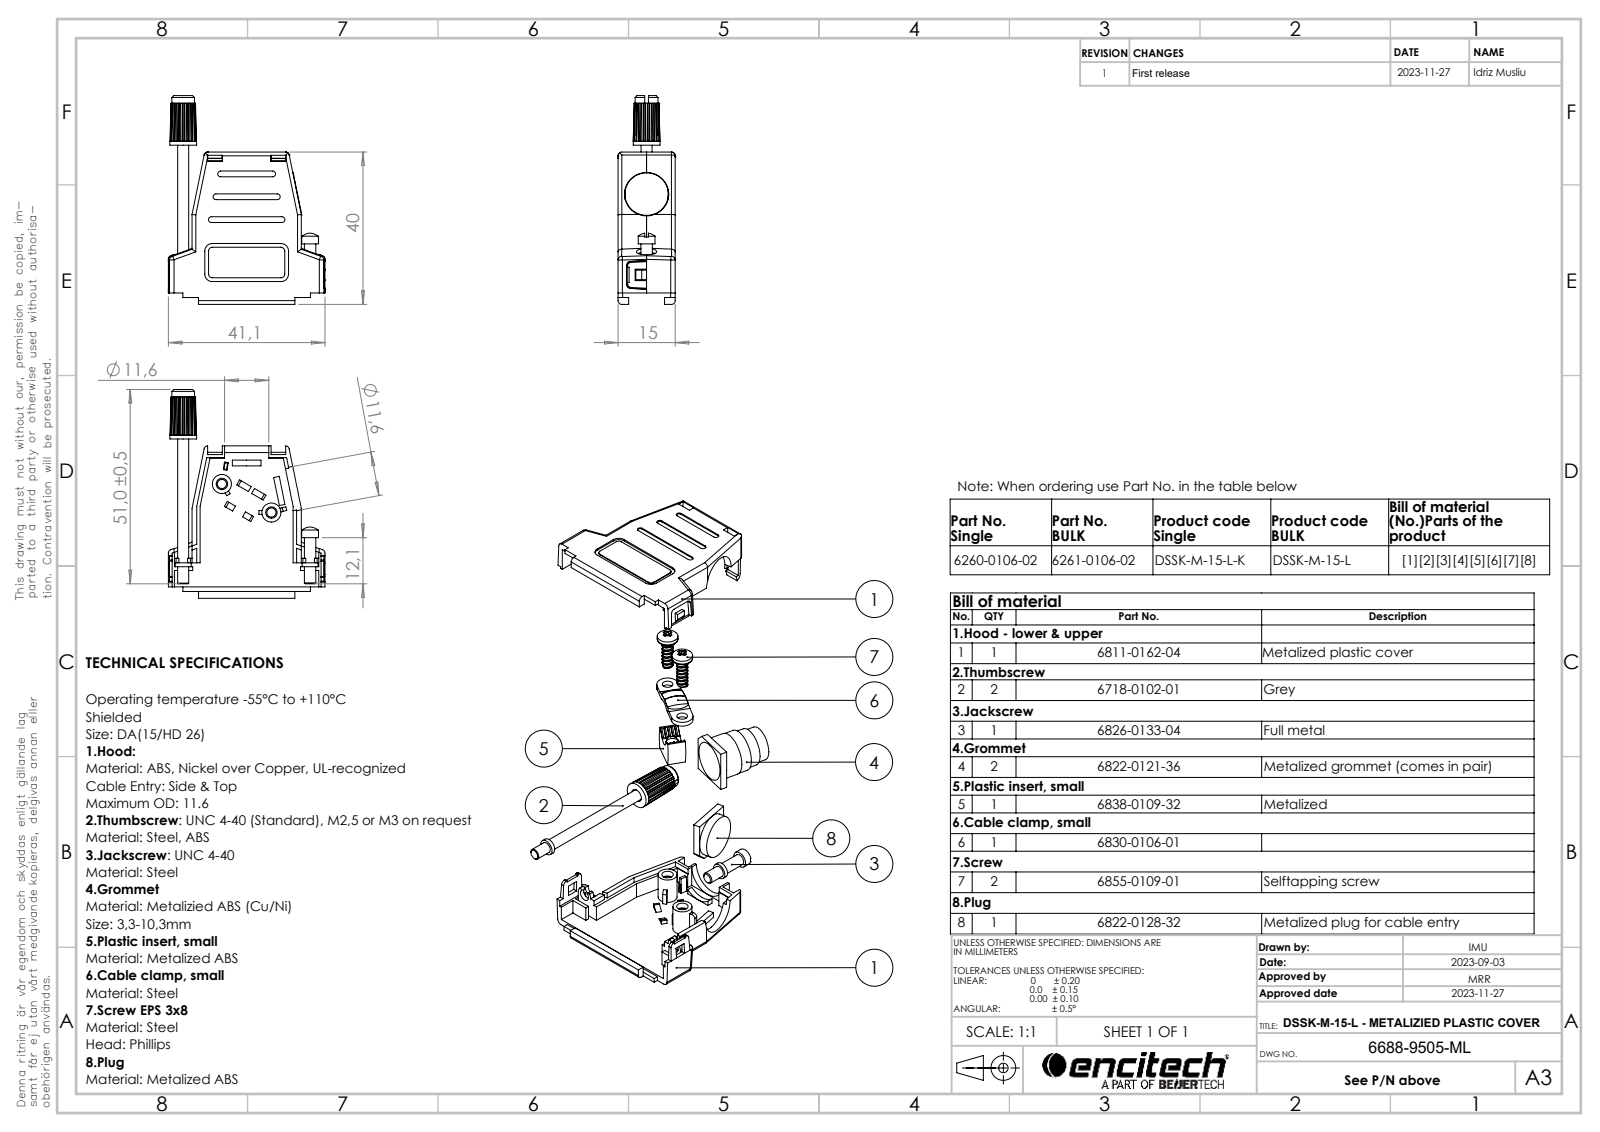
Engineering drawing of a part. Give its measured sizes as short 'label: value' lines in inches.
name: 6855-0109-01; 6830-0106-01; 6718-0102-01; 6822-0121 part 1 (+6 more)
written by: SolidWorks 2021 (AUTOMOTIVE_DESIGN)
unit: in
bodies: 12 solids, 1044 faces (700 planar, 256 cylindrical, 88 other)
size: 2.157 × 1.618 × 0.591
volume: 0.487 in³; area: 19.64 in²
holes: 2× ⌀0.094, 2× ⌀0.11, 2× ⌀0.118, 2× ⌀0.457, 1× ⌀0.03, 1× ⌀0.035, 1× ⌀0.049, 1× ⌀0.098, 1× ⌀0.138, 1× ⌀0.295, 1× ⌀0.335, 1× ⌀0.37
bosses: 2× ⌀0.215, 2× ⌀0.197, 2× ⌀0.165, 1× ⌀0.449, 1× ⌀0.445, 1× ⌀0.437, 1× ⌀0.398, 1× ⌀0.358
rounds: 31× R0.039, 24× R0.01, 20× R0.02, 16× R0.005, 6× R0.03, 6× R0.079, 4× R0.016, 4× R0.047
face distances: 0.524, 0.067, 0.457, 0.591, 0.295, 0.287, 0.228, 0.059, 0.047, 0.039
hole spacings: 0.295, 0.298, 0.298, 0.307, 0.323, 0.343, 0.344, 0.365
